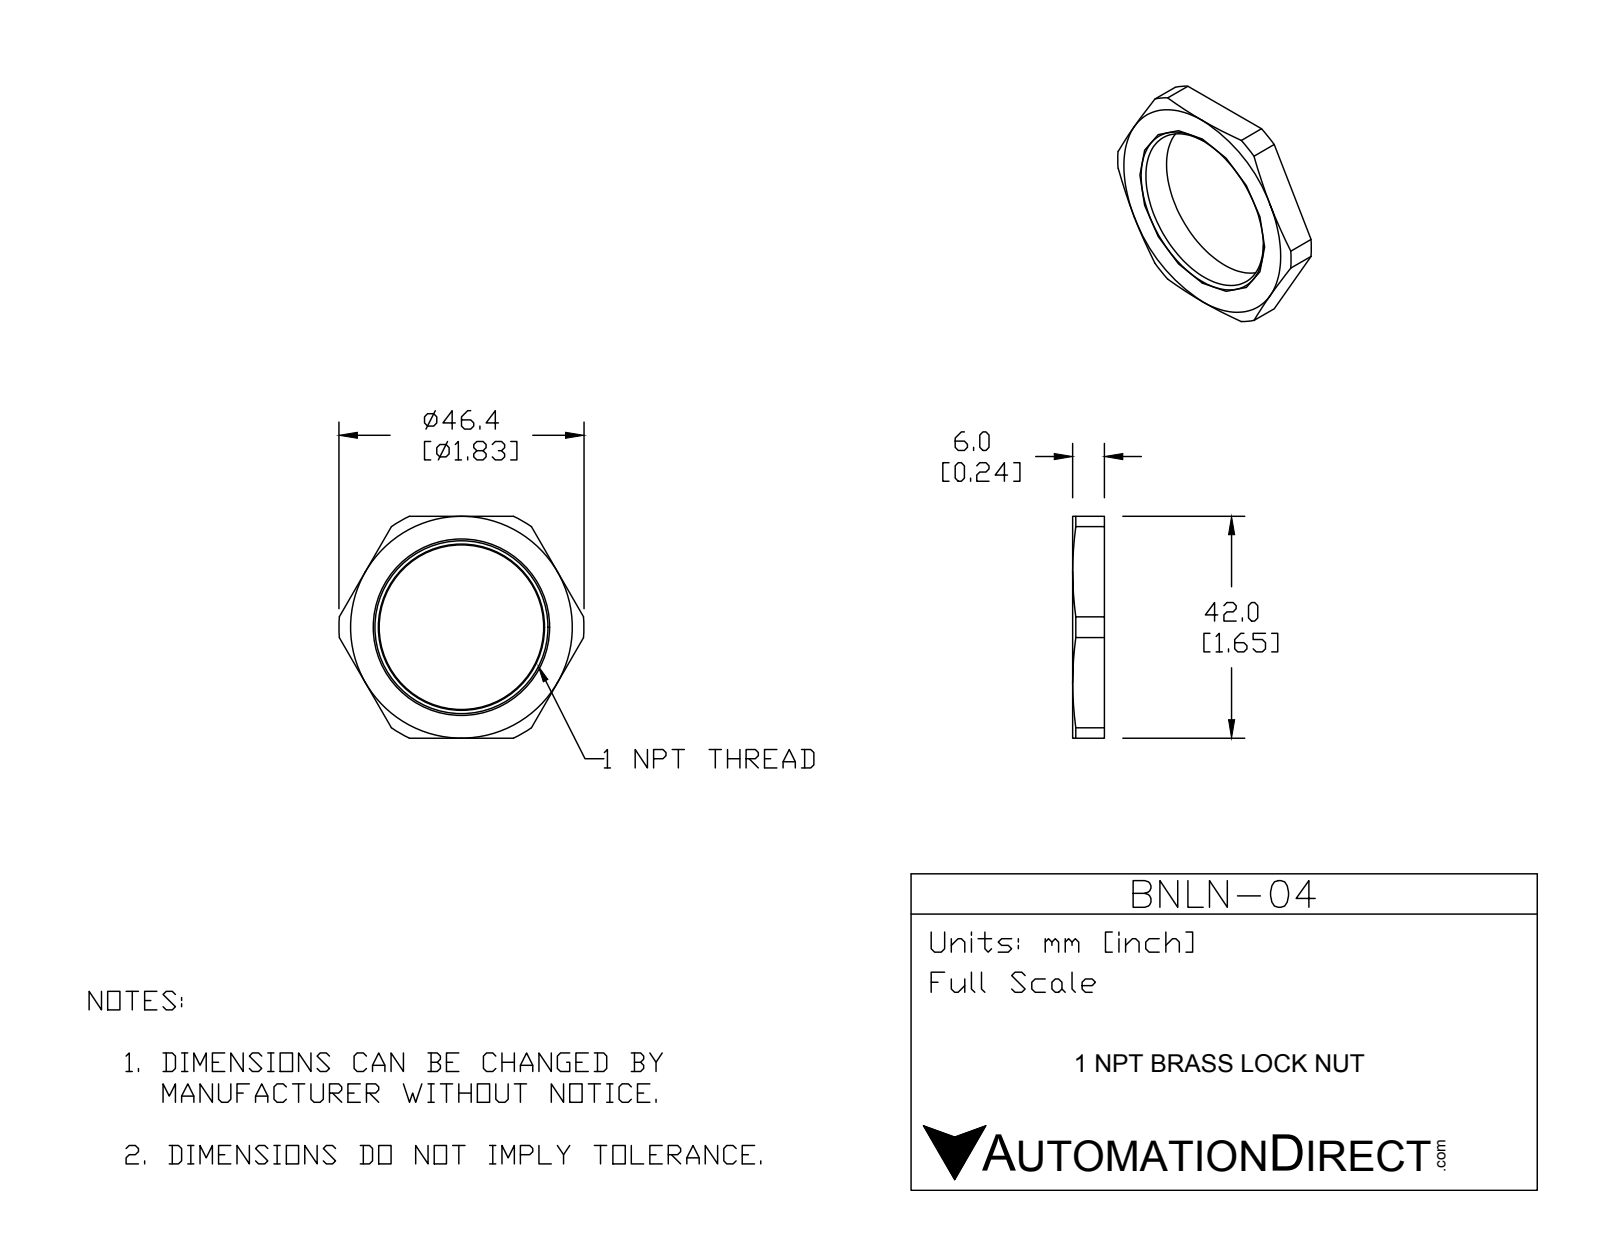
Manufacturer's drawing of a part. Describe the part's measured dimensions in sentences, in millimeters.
The part is named "BNLN-04". Its 3-D file was written by "SolidWorks 2015 (CONFIG_CONTROL_DESIGN)". It is 1 solid with 25 faces: 8 planar, 7 cylindrical and 10 other. Overall it measures 46.4 by 42 by 6 millimeters. Its volume is 4 423 cubic millimeters and its surface area 2 865 square millimeters. Partial cylindrical surfaces (rounded edges, fillets, slot ends): 1 of radius 23.2. The main face-to-face distances are 6, 42.
